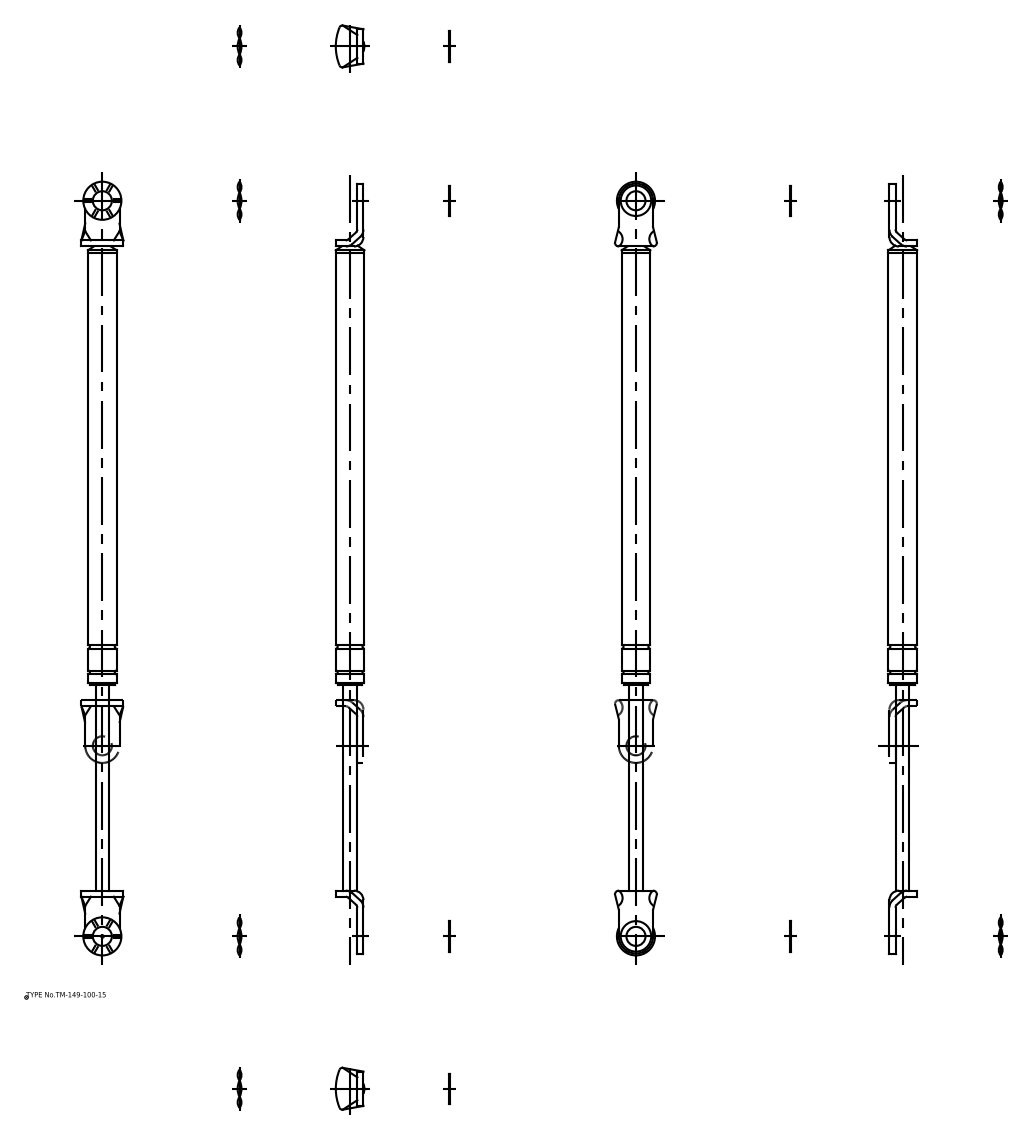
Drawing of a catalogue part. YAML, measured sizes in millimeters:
part_name: "washer_2; washer_1; body_div"
step_written_by: "spGate 16.7.1 (AUTOMOTIVE_DESIGN)"
units: millimeters
bodies: {solids: 6, faces: 92, planar: 44, cylindrical: 42, other: 6}
overall_size: [406, 22, 15.4]
volume: 50095
surface_area: 19092
round_holes:
  - {diameter: 10, count: 2}
round_bosses_or_shafts:
  - {diameter: 20, count: 2}
  - {diameter: 16, count: 2}
  - {diameter: 15.4, count: 1}
  - {diameter: 15, count: 1}
  - {diameter: 13, count: 1}
  - {diameter: 7, count: 1}
partial_cylinders:
  - {radius: 2, count: 2}
  - {radius: 5, count: 2}
  - {radius: 9, count: 2}
  - {radius: 17.12, count: 1}
face_to_face_distances: [3.2, 2, 5.2, 341.2, 0.5, 3.7, 5.7, 344.4, 111.2, 233.2]
hole_center_spacings: [386]
